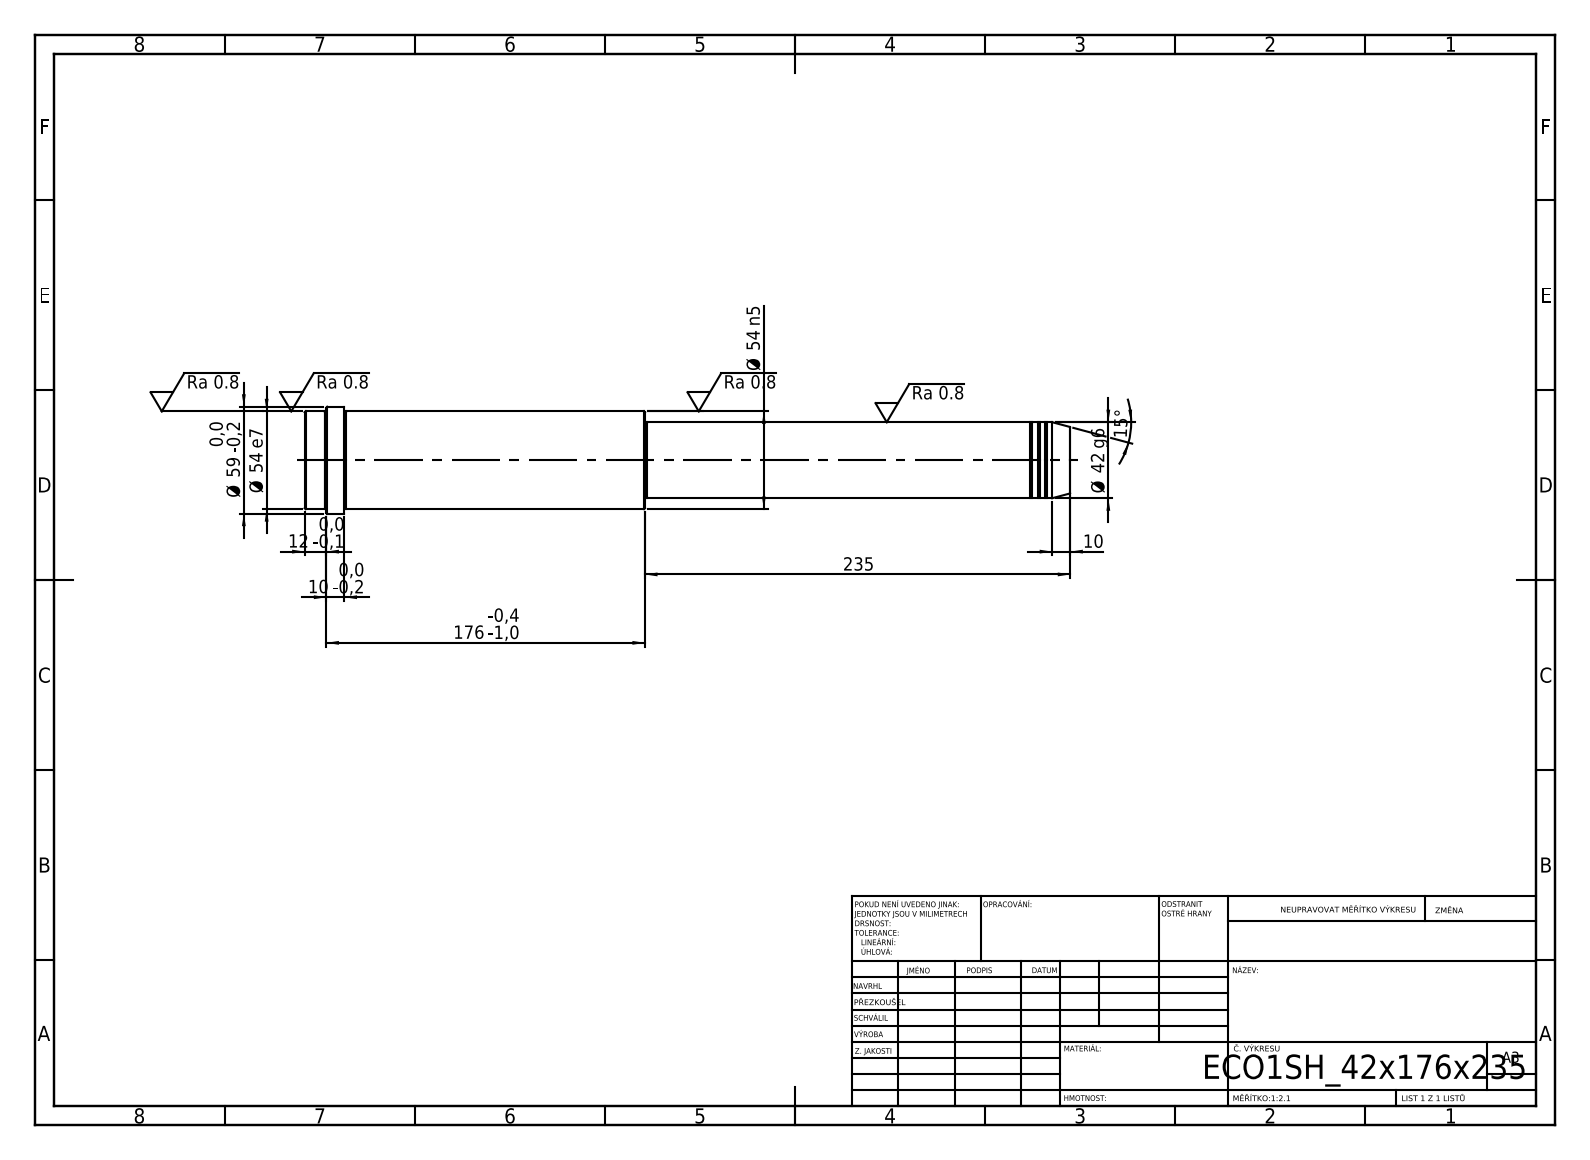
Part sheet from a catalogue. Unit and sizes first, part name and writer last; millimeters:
Units: millimetres
Overall size (bounding box): 423 × 59 × 59
Round bosses / shafts (diameter × count): ⌀59 ×1, ⌀54 ×1, ⌀42 ×1, ⌀41 ×1
Main face-to-face distances: 423, 235, 188, 401, 166, 22, 411, 176, 10, 12
Volume: 758 466 mm³ · Surface area: 68 518 mm²
Bodies: 1 solid, 52 faces (6 planar, 16 cylindrical, 30 other)
STEP written by: SolidWorks 2019 (CONFIG_CONTROL_DESIGN)
